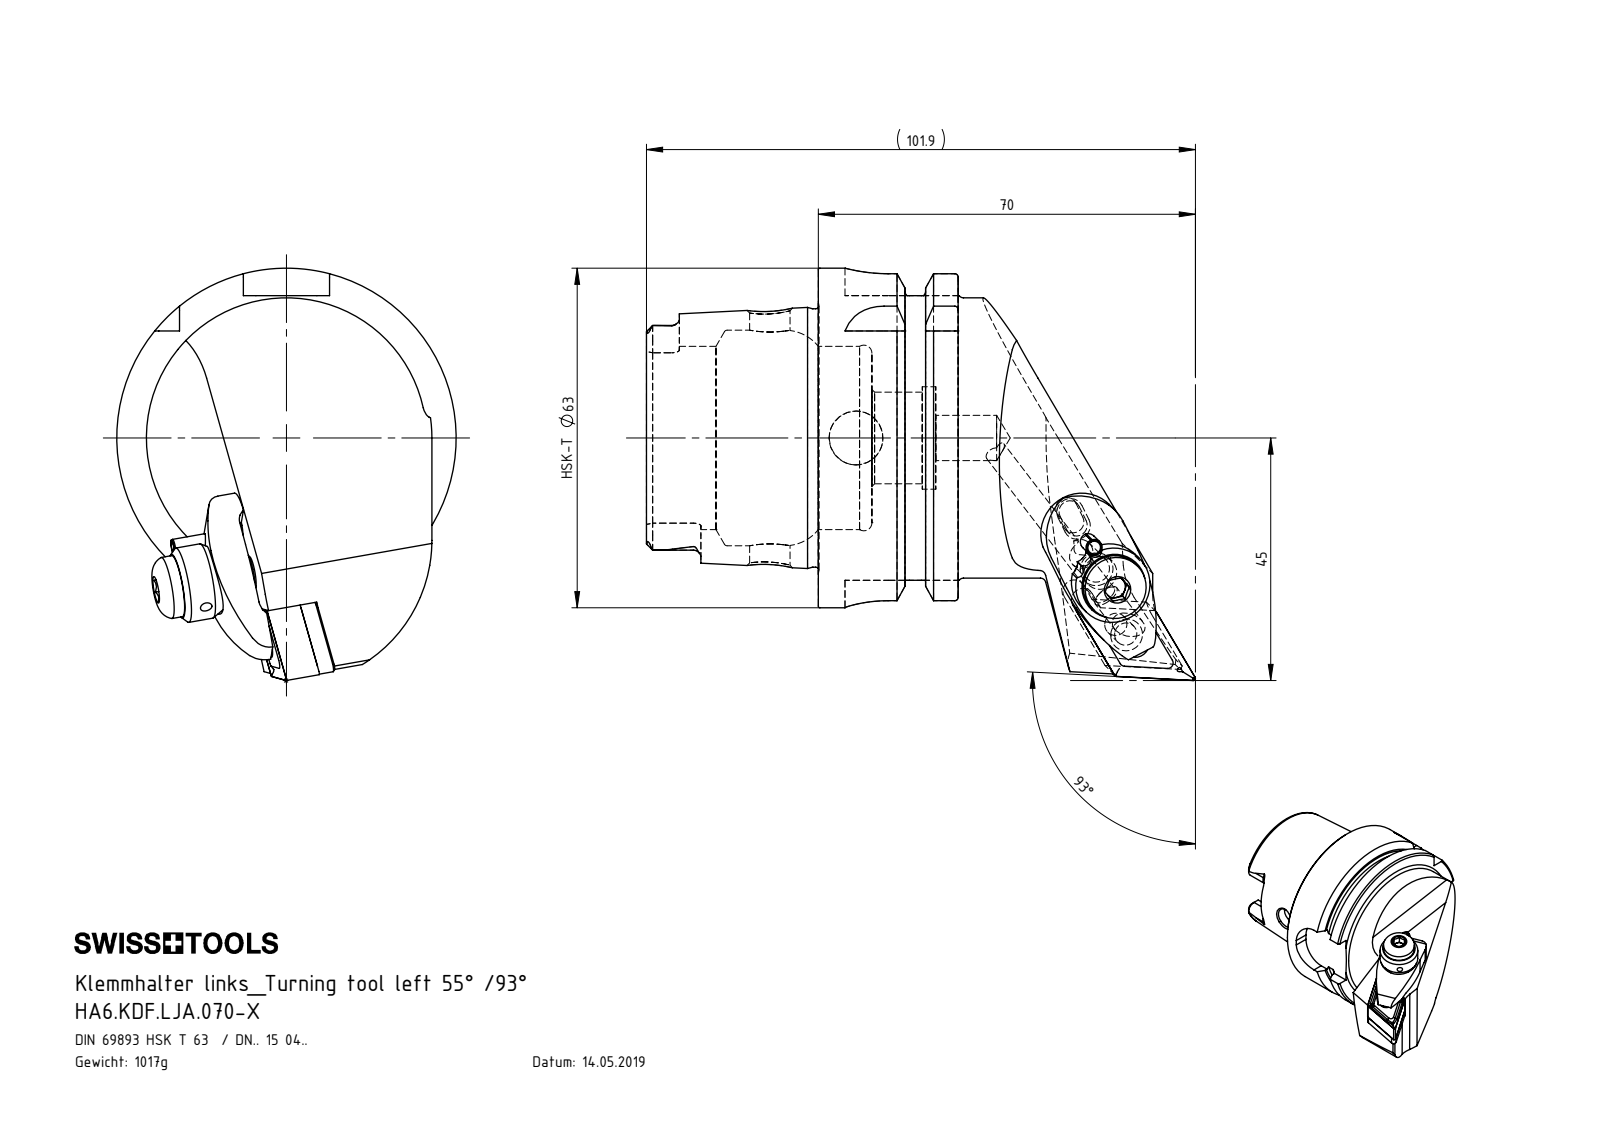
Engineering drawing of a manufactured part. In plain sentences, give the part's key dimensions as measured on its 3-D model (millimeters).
The part is named "WCC-ER5.102.012_B; WCC-ER5.102.005_A; DNMG150604; ISO 13337 - 3 x 12 (+8 more)". Its 3-D file was written by "SolidWorks 2017 (AUTOMOTIVE_DESIGN)". It is 11 solids with 466 faces: 127 planar, 151 cylindrical and 188 other. Overall it measures 101.9 by 76.5 by 63 millimeters. Its volume is 130 480 cubic millimeters and its surface area 34 145 square millimeters. Round holes: 3 of diameter 2, 2 of diameter 4.2, 2 of diameter 5, 2 of diameter 7, 1 of diameter 2.4, 1 of diameter 3, 1 of diameter 4, 1 of diameter 5.16, 1 of diameter 6.2, 1 of diameter 6.4, 1 of diameter 7.5, 1 of diameter 8.4. Round bosses or shafts: 2 of diameter 5, 2 of diameter 3, 1 of diameter 63, 1 of diameter 54.95, 1 of diameter 52, 1 of diameter 47.94, 1 of diameter 14, 1 of diameter 11.5. Partial cylindrical surfaces (rounded edges, fillets, slot ends): 6 of radius 0.39, 6 of radius 1.4, 4 of radius 0.4, 4 of radius 1, 4 of radius 8, 3 of radius 0.69, 3 of radius 0.69, 3 of radius 1.5. The main face-to-face distances are 25.95, 16, 9.95, 31.9, 41.85, 57.85, 6.05, 52.8, 3.18, 9.23. The hole center spacings are 23, 8, 8.01, 8.2, 14.8, 14.99, 15.
